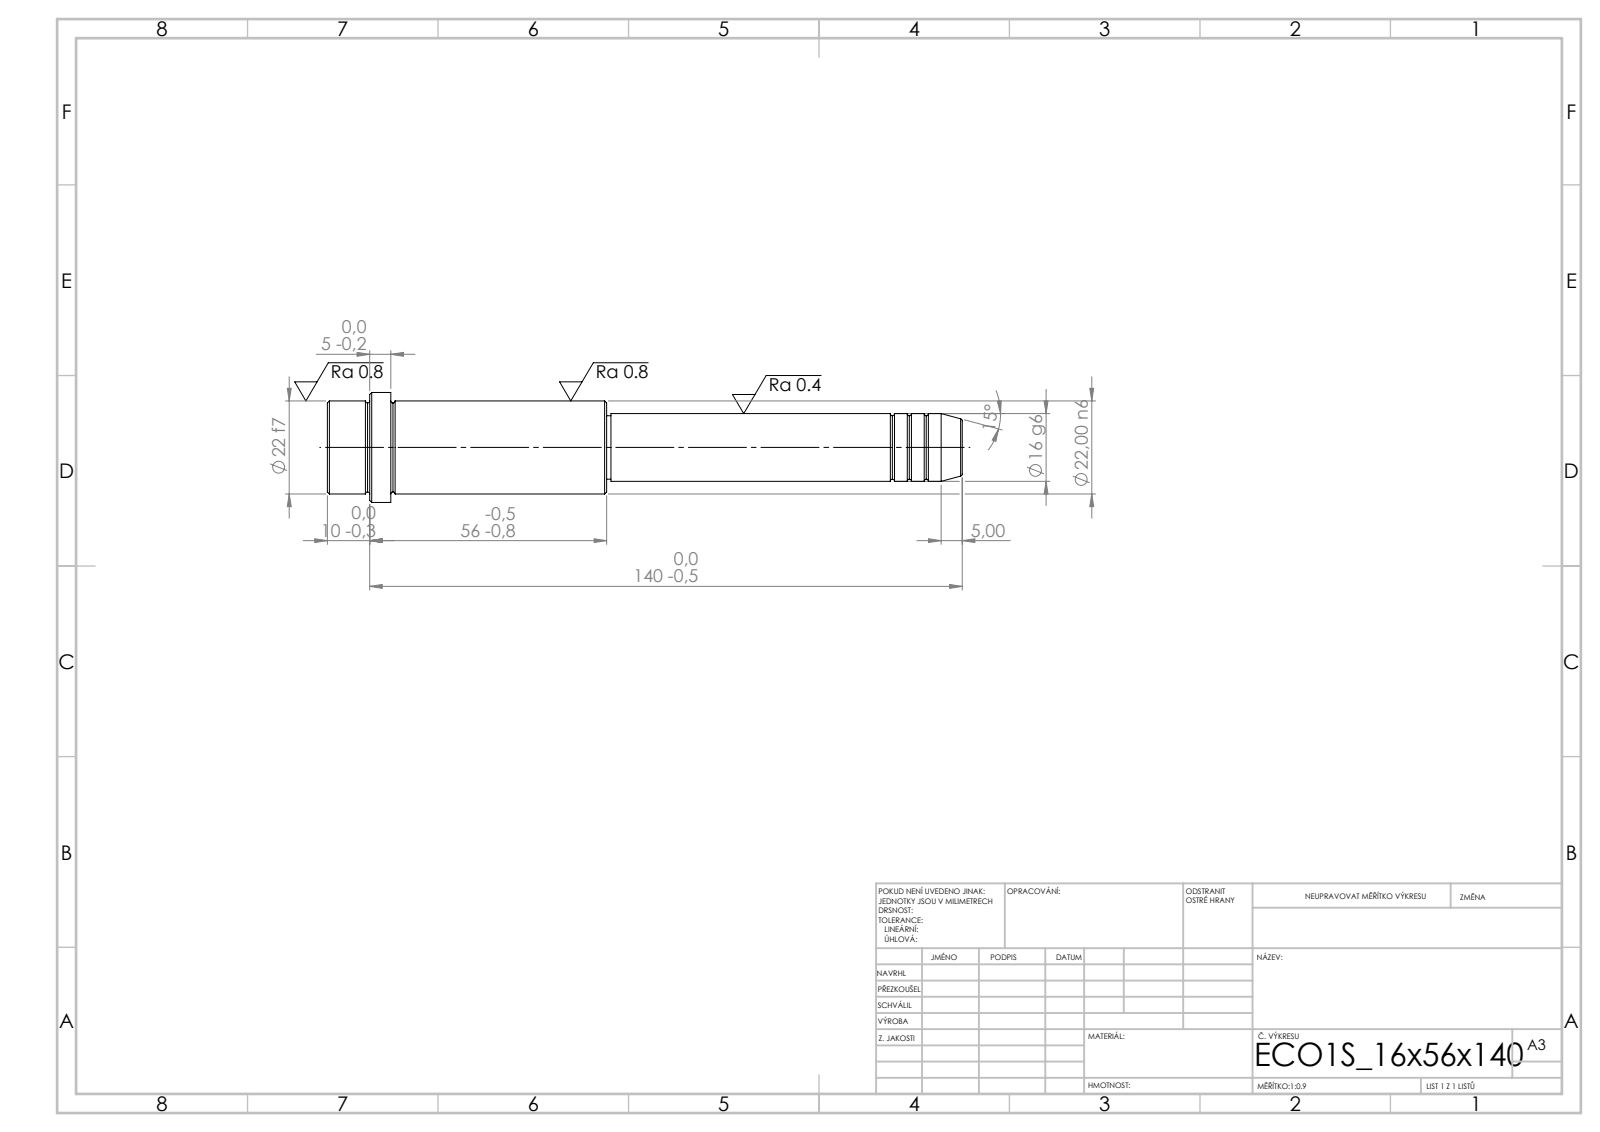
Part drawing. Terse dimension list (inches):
written by: SolidWorks 2019 (CONFIG_CONTROL_DESIGN)
unit: in
bodies: 1 solid, 52 faces (6 planar, 16 cylindrical, 30 other)
size: 5.906 × 1.024 × 1.024
volume: 2.588 in³; area: 15.44 in²
bosses: 1× ⌀1.024, 1× ⌀0.866, 1× ⌀0.63, 1× ⌀0.591
face distances: 2.598, 2.008, 0.591, 3.307, 5.315, 5.906, 5.512, 2.205, 0.197, 0.394
